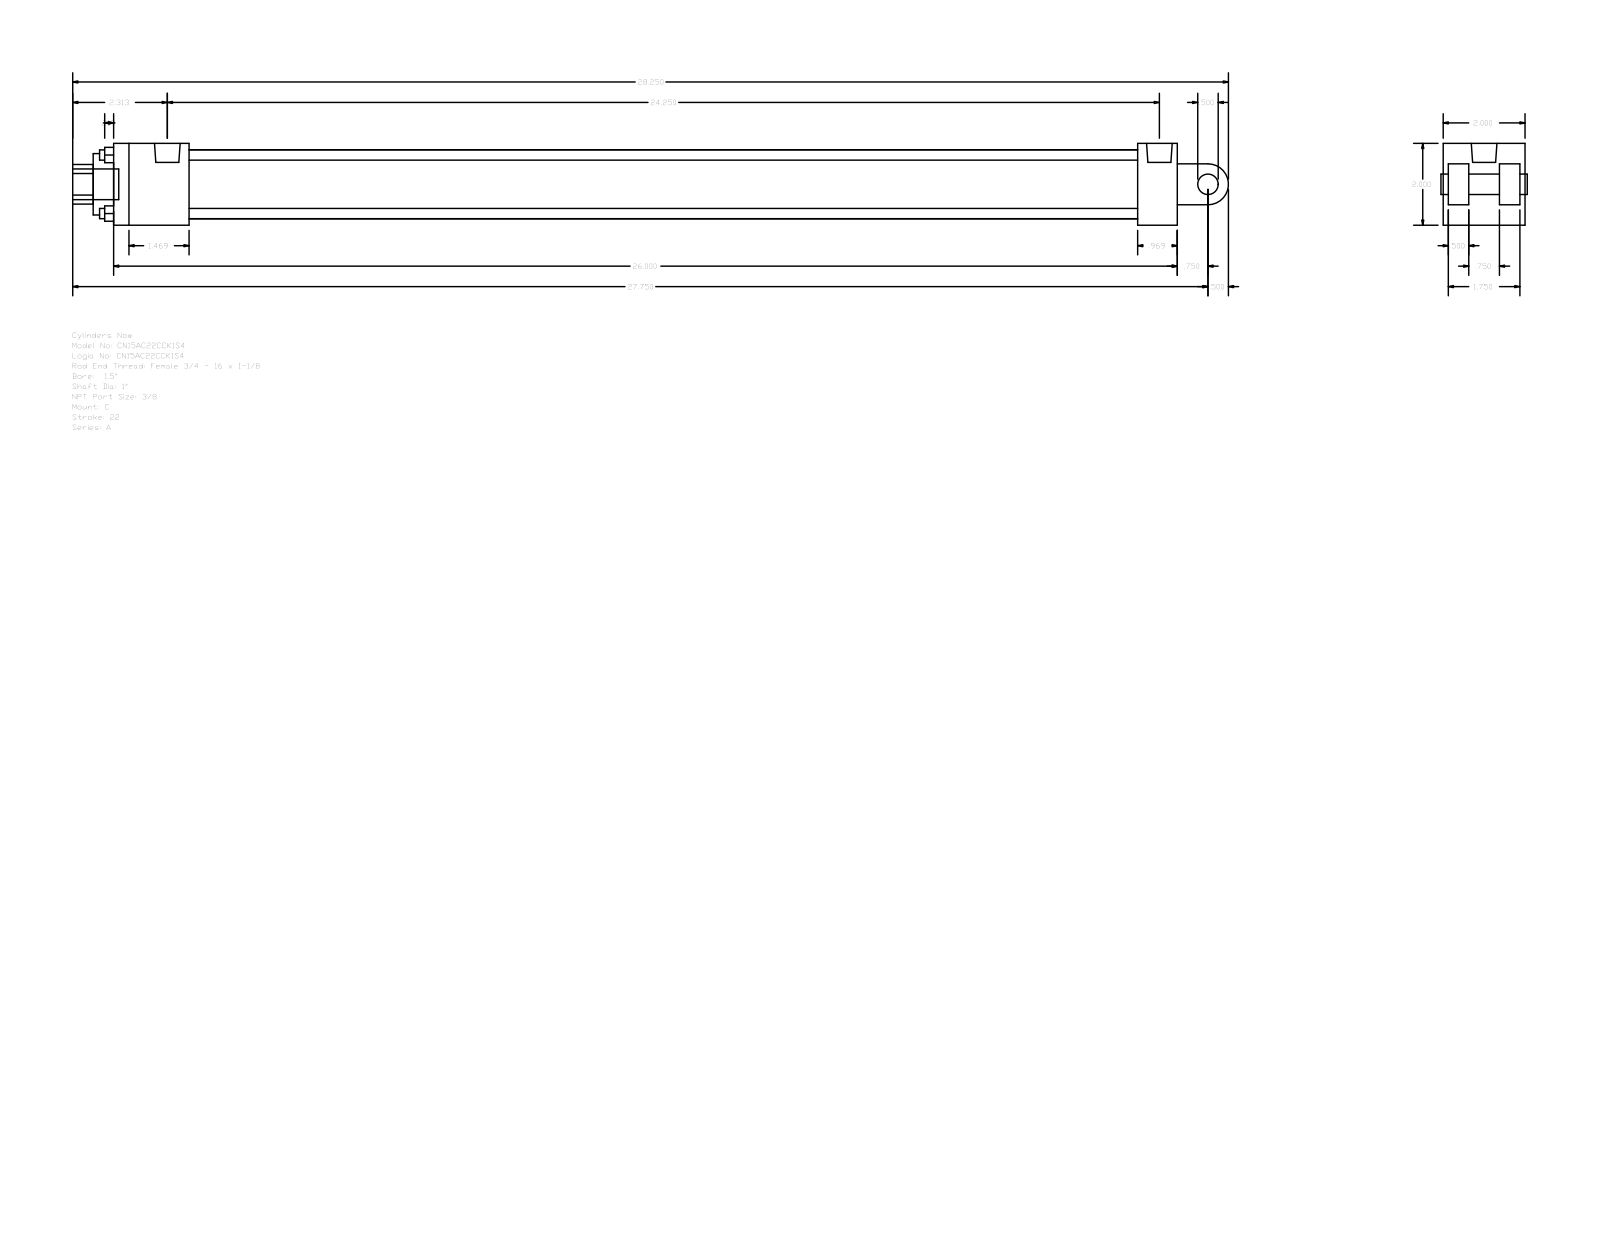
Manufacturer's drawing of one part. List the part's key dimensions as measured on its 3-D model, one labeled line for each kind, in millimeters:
Part name (STEP PRODUCT): A_C__0150_1
STEP written by: GSSL Pune (CONFIG_CONTROL_DESIGN)
Units: millimetres
Bodies: 0 solids, 99 faces (70 planar, 29 cylindrical, 0 other)
Overall size (bounding box): 717.55 × 50.8 × 50.8
Round holes (diameter × count): ⌀6.35 ×4, ⌀5.56 ×2, ⌀15.93 ×1, ⌀25.4 ×1, ⌀38.1 ×1, ⌀42.93 ×1
Round bosses / shafts (diameter × count): ⌀5.56 ×2, ⌀19.05 ×1, ⌀15.93 ×1, ⌀12.7 ×1
Partial cylindrical surfaces — rounded edges, fillets, slot ends (radius × count): R12.29 ×1, R12.7 ×1
Main face-to-face distances: 50.8, 12.7, 3.17, 15.87, 47.63, 34.93, 31.76, 660.4, 635.79, 24.61
Hole centre spacings: 25.68, 36.32, 51.36, 3.97
